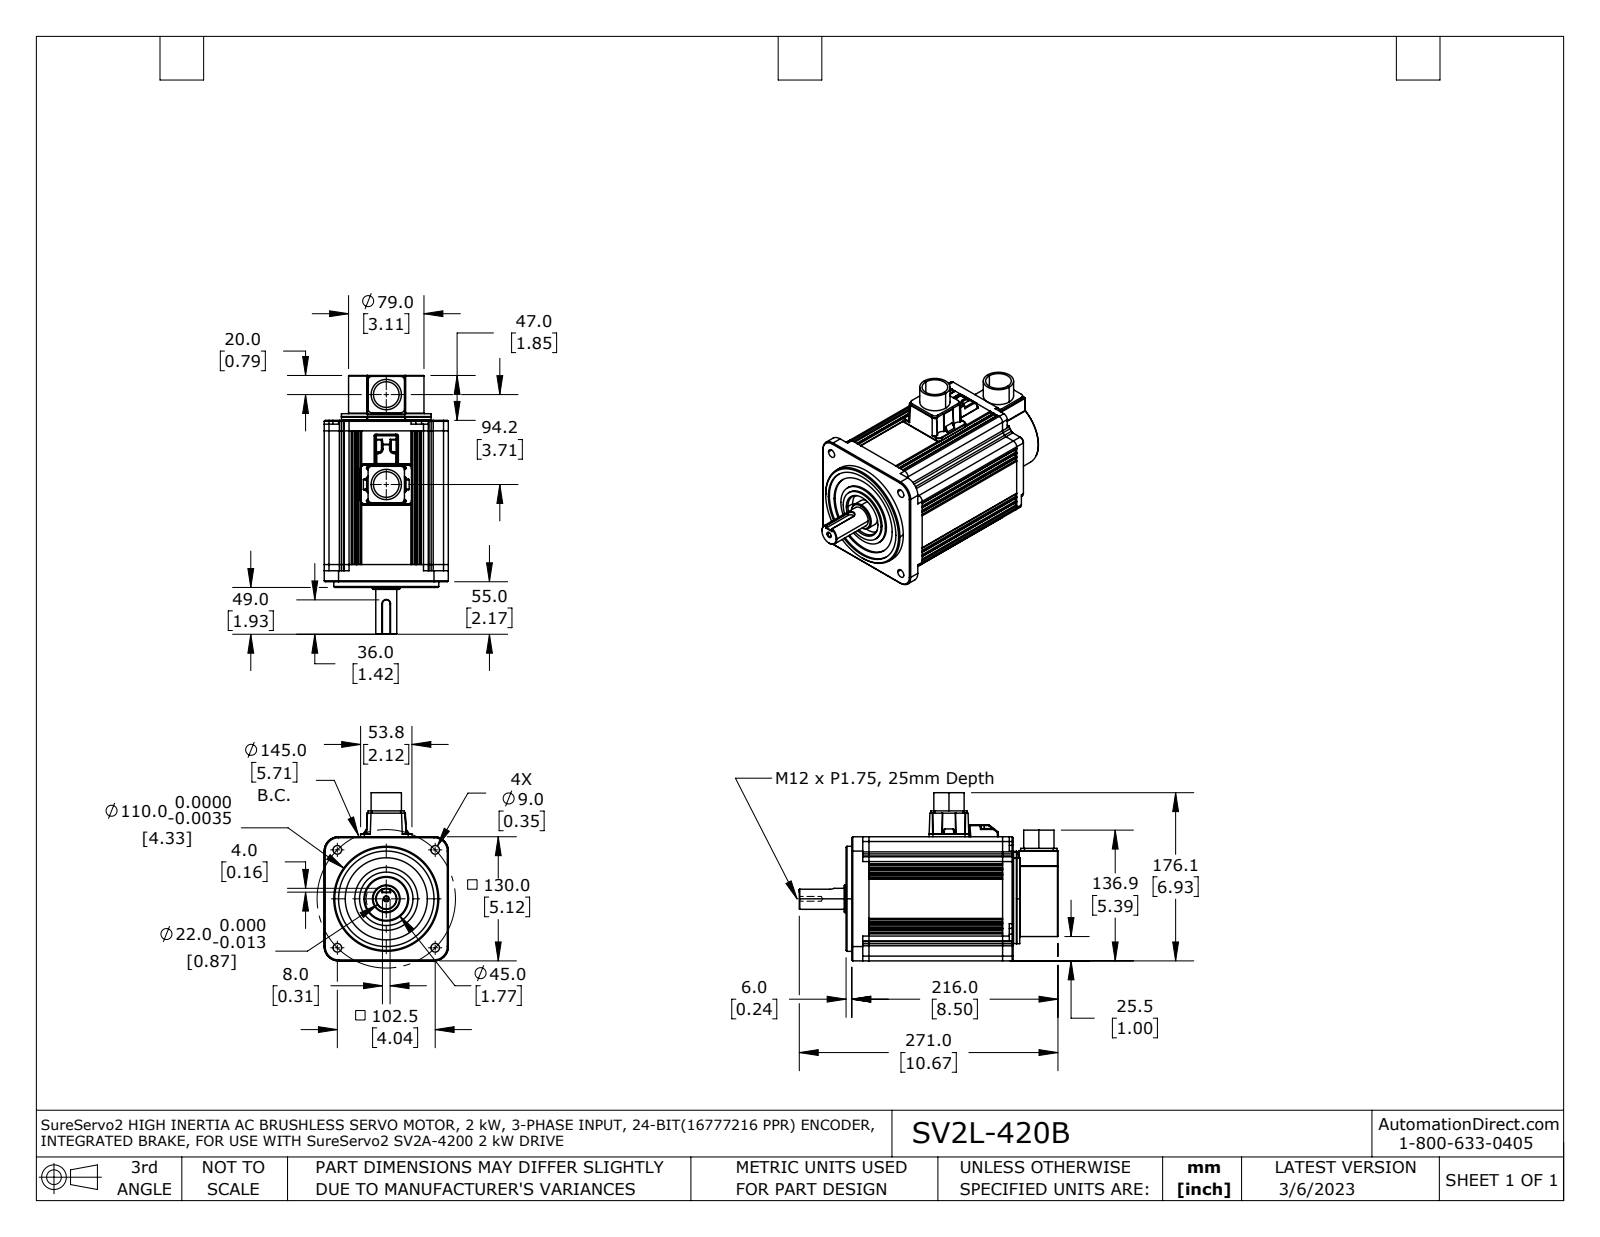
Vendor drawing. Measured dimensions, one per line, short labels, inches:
name: SV2L-420B
written by: SolidWorks 2021 (AUTOMOTIVE_DESIGN)
unit: in
bodies: 1 solid, 658 faces (290 planar, 215 cylindrical, 153 other)
size: 10.669 × 6.935 × 5.118
volume: 177.8 in³; area: 269.3 in²
holes: 4× ⌀0.354, 2× ⌀1.058, 1× ⌀0.197, 1× ⌀1.772, 1× ⌀3.386, 1× ⌀3.937
bosses: 2× ⌀1.25, 1× ⌀4.331, 1× ⌀3.701, 1× ⌀3.11, 1× ⌀2.598, 1× ⌀2.205, 1× ⌀1.142, 1× ⌀0.866
rounds: 87× R0.039, 34× R0.02, 17× R0.157, 8× R0.118, 8× R0.197, 2× R0.079
face distances: 0.827, 4.291, 5.118, 2.402, 0.211, 0.959, 6.654, 3.465, 1.85, 8.504
hole spacings: 2.855, 4.037, 5.709, 3.708
